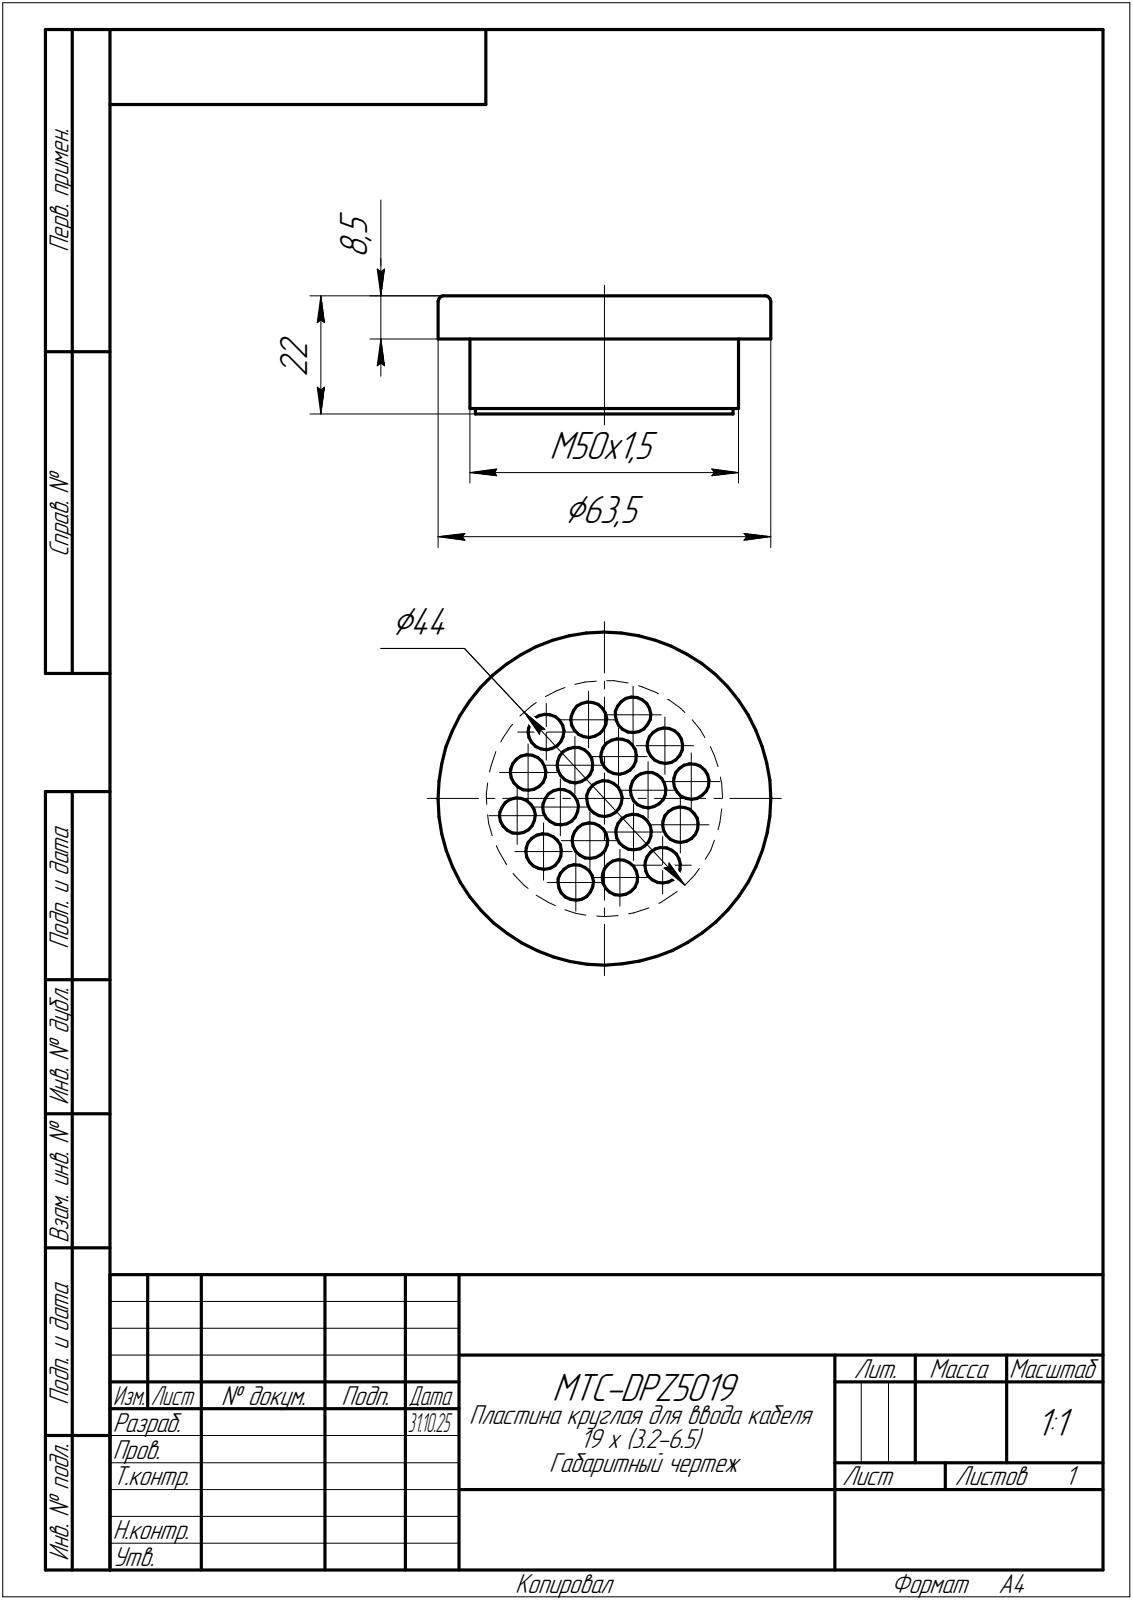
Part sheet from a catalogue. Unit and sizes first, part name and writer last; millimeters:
Units: millimetres
Overall size (bounding box): 62 × 62 × 22
Round holes (diameter × count): ⌀6.63 ×19, ⌀44 ×1
Round bosses / shafts (diameter × count): ⌀62 ×1, ⌀50 ×1, ⌀48 ×1
Main face-to-face distances: 8, 7.5, 0.5, 14, 21.5, 22, 1, 13, 20.5, 21
Hole centre spacings: 16.5, 22.57, 15, 21.86, 30.43, 8.29, 8.3, 8.85
Volume: 29 831 mm³ · Surface area: 12 724 mm²
Bodies: 2 solids, 48 faces (24 planar, 23 cylindrical, 1 other)
Part name (STEP PRODUCT): MTC-DPZ5019; 43758_PART1; 43758_PART2
STEP written by: C3D Toolkit (CONFIG_CONTROL_DESIGN)
